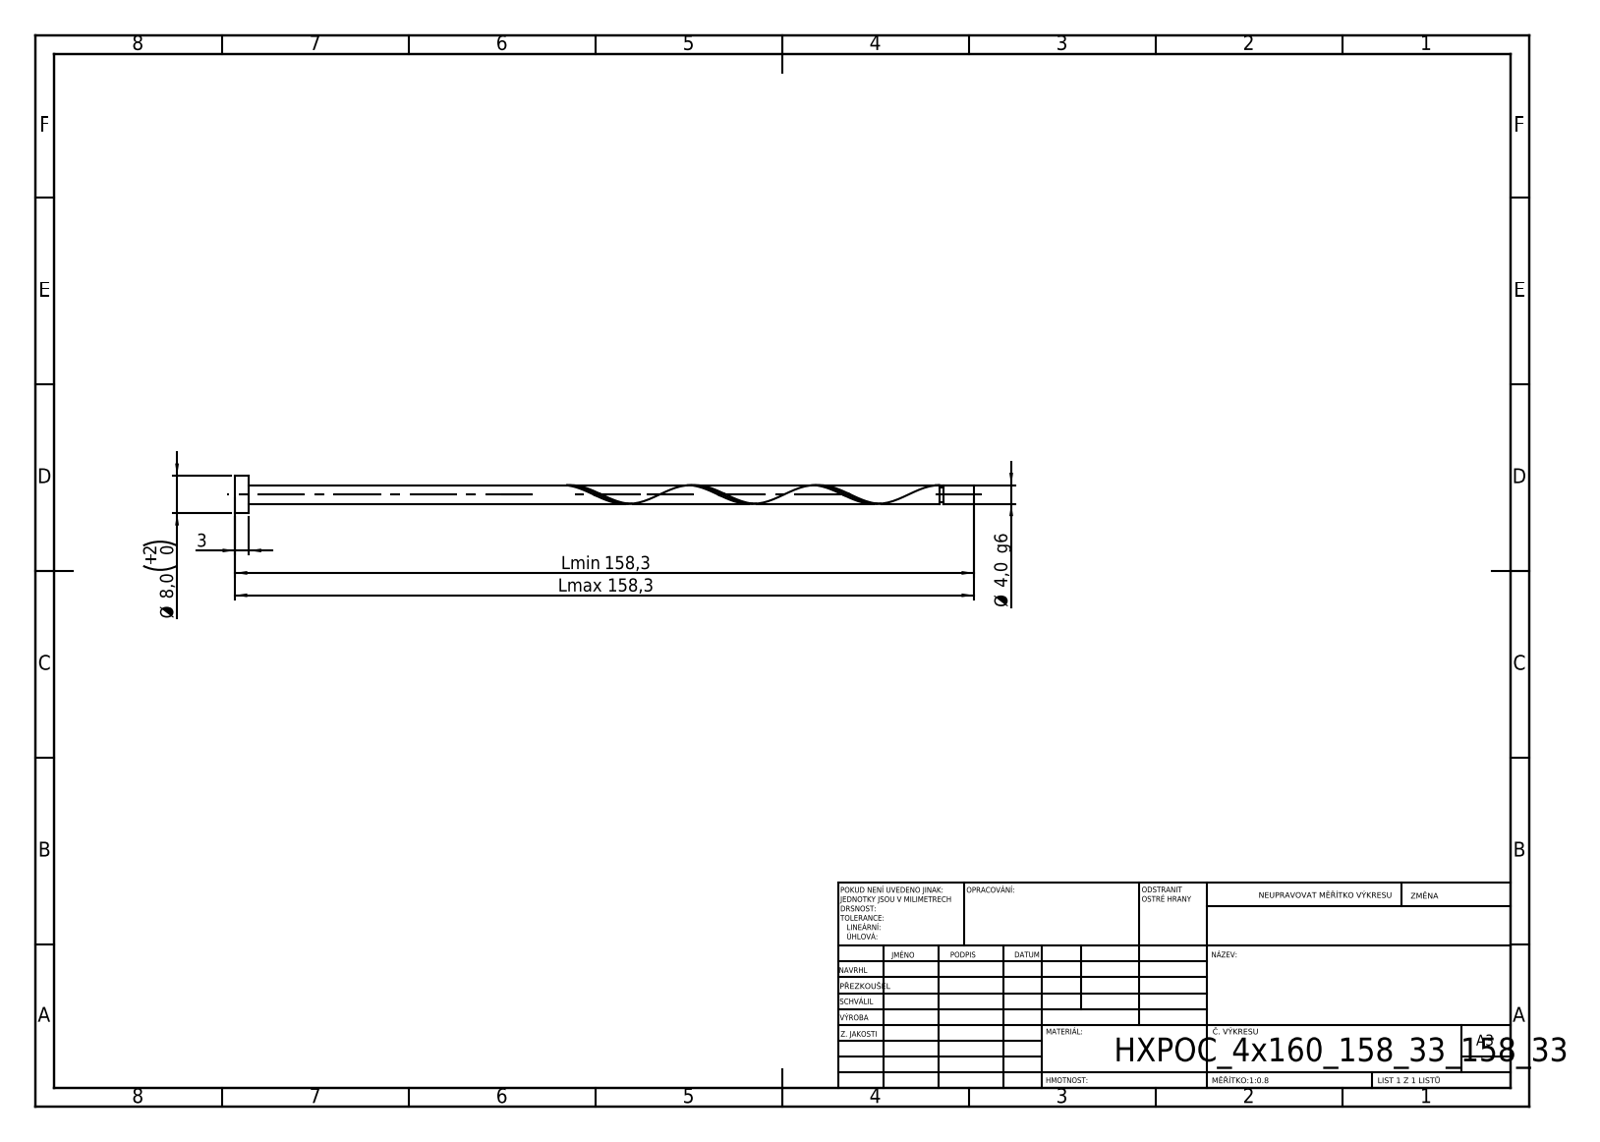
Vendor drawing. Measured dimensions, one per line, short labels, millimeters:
written by: SolidWorks 2019 (CONFIG_CONTROL_DESIGN)
unit: mm
bodies: 1 solid, 21 faces (6 planar, 14 cylindrical, 1 other)
size: 158.33 × 8 × 8
volume: 2 080 mm³; area: 2 170 mm²
bosses: 1× ⌀8, 1× ⌀4, 1× ⌀3.2
face distances: 3, 158.33, 155.33, 151.8, 148.8, 6.53, 151, 148, 0.8, 7.33
